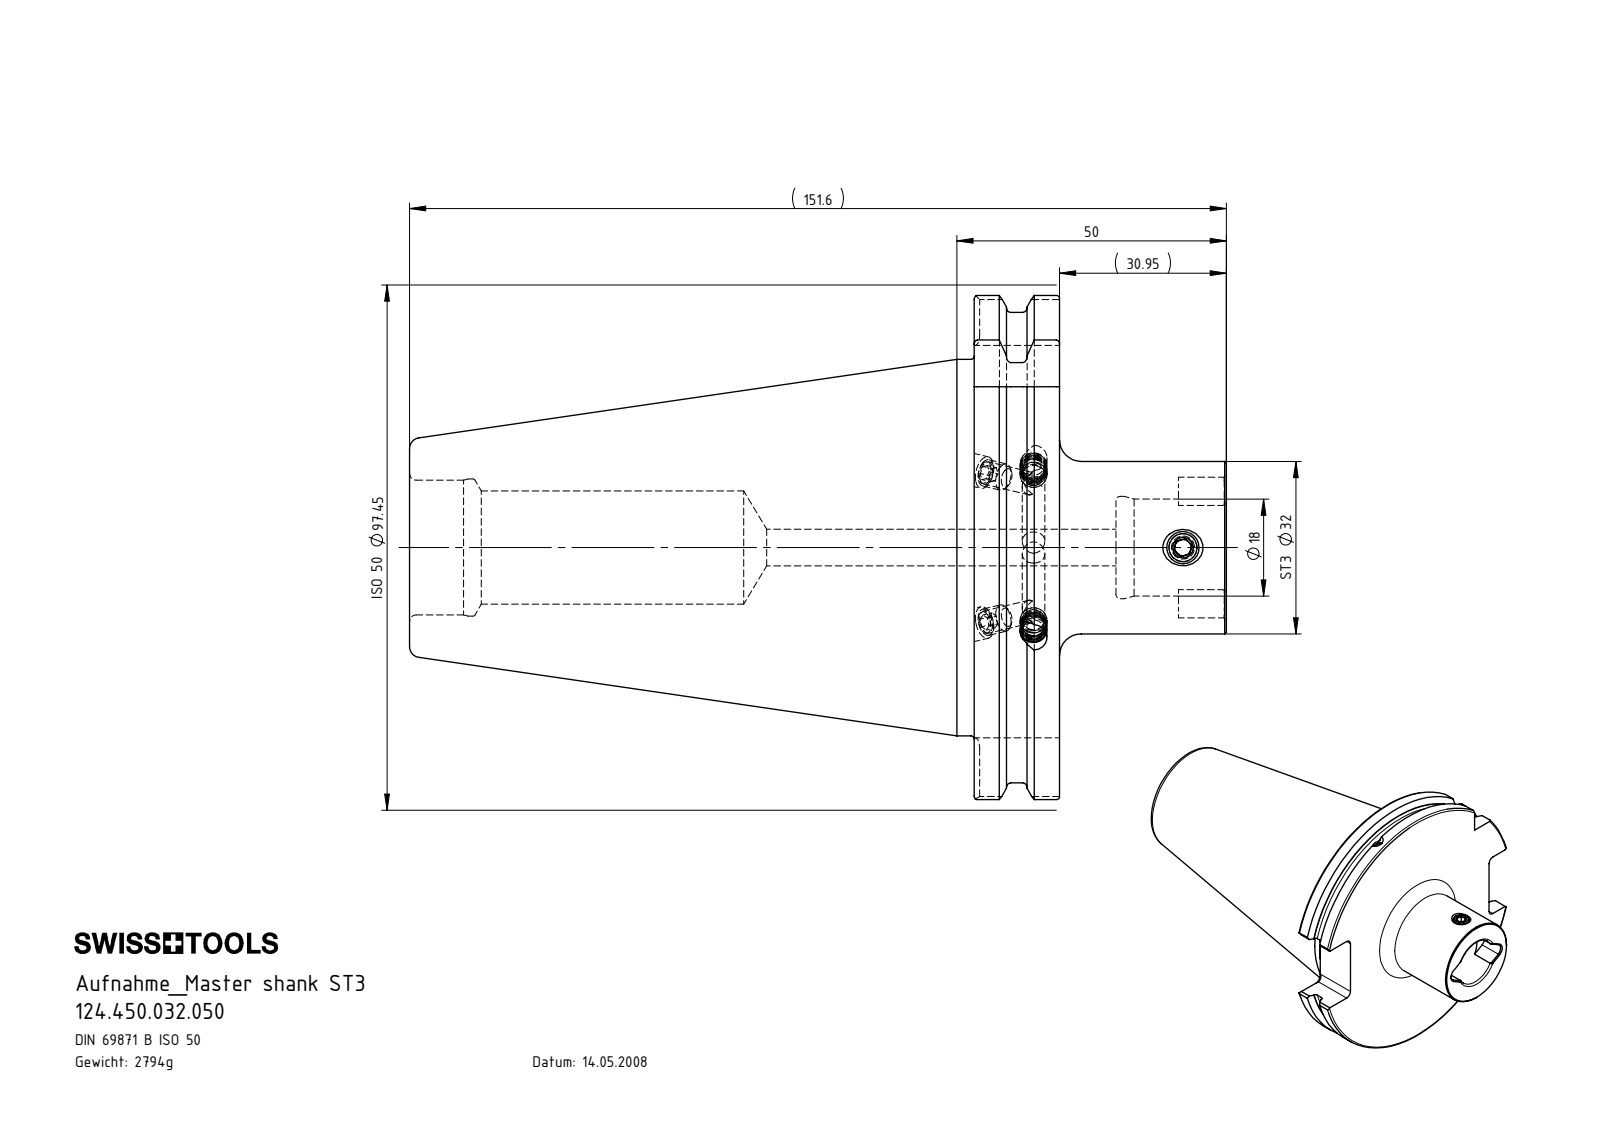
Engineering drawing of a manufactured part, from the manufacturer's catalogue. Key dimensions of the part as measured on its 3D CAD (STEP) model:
Part name (STEP PRODUCT): ISO 4026 - M5 x 5_PreviewCfg; ST3-ER1.001.008_A; SB5.ST3.K01.050; SB5-ST3.K01.050_C_mit Bundkhlung (+1 more)
STEP written by: SolidWorks 2017 (AUTOMOTIVE_DESIGN)
Units: millimetres
Bodies: 8 solids, 206 faces (78 planar, 46 cylindrical, 82 other)
Overall size (bounding box): 151.6 × 97.45 × 93.51
Volume: 355 908 mm³ · Surface area: 47 582 mm²
Round holes (diameter × count): ⌀4.2 ×3, ⌀4 ×2, ⌀6 ×2, ⌀3 ×1, ⌀5 ×1, ⌀5.25 ×1, ⌀6.8 ×1, ⌀18 ×1, ⌀19 ×1, ⌀21 ×1, ⌀25 ×1, ⌀25.45 ×1
Round bosses / shafts (diameter × count): ⌀5 ×3, ⌀91 ×1, ⌀69.85 ×1, ⌀32 ×1, ⌀6 ×1
Partial cylindrical surfaces — rounded edges, fillets, slot ends (radius × count): R2 ×8, R2.5 ×2, R48.73 ×1
Main face-to-face distances: 15.85, 104.8, 120.65, 151.6, 46.8, 30.95, 72.8, 25.7, 131.1, 26.3
